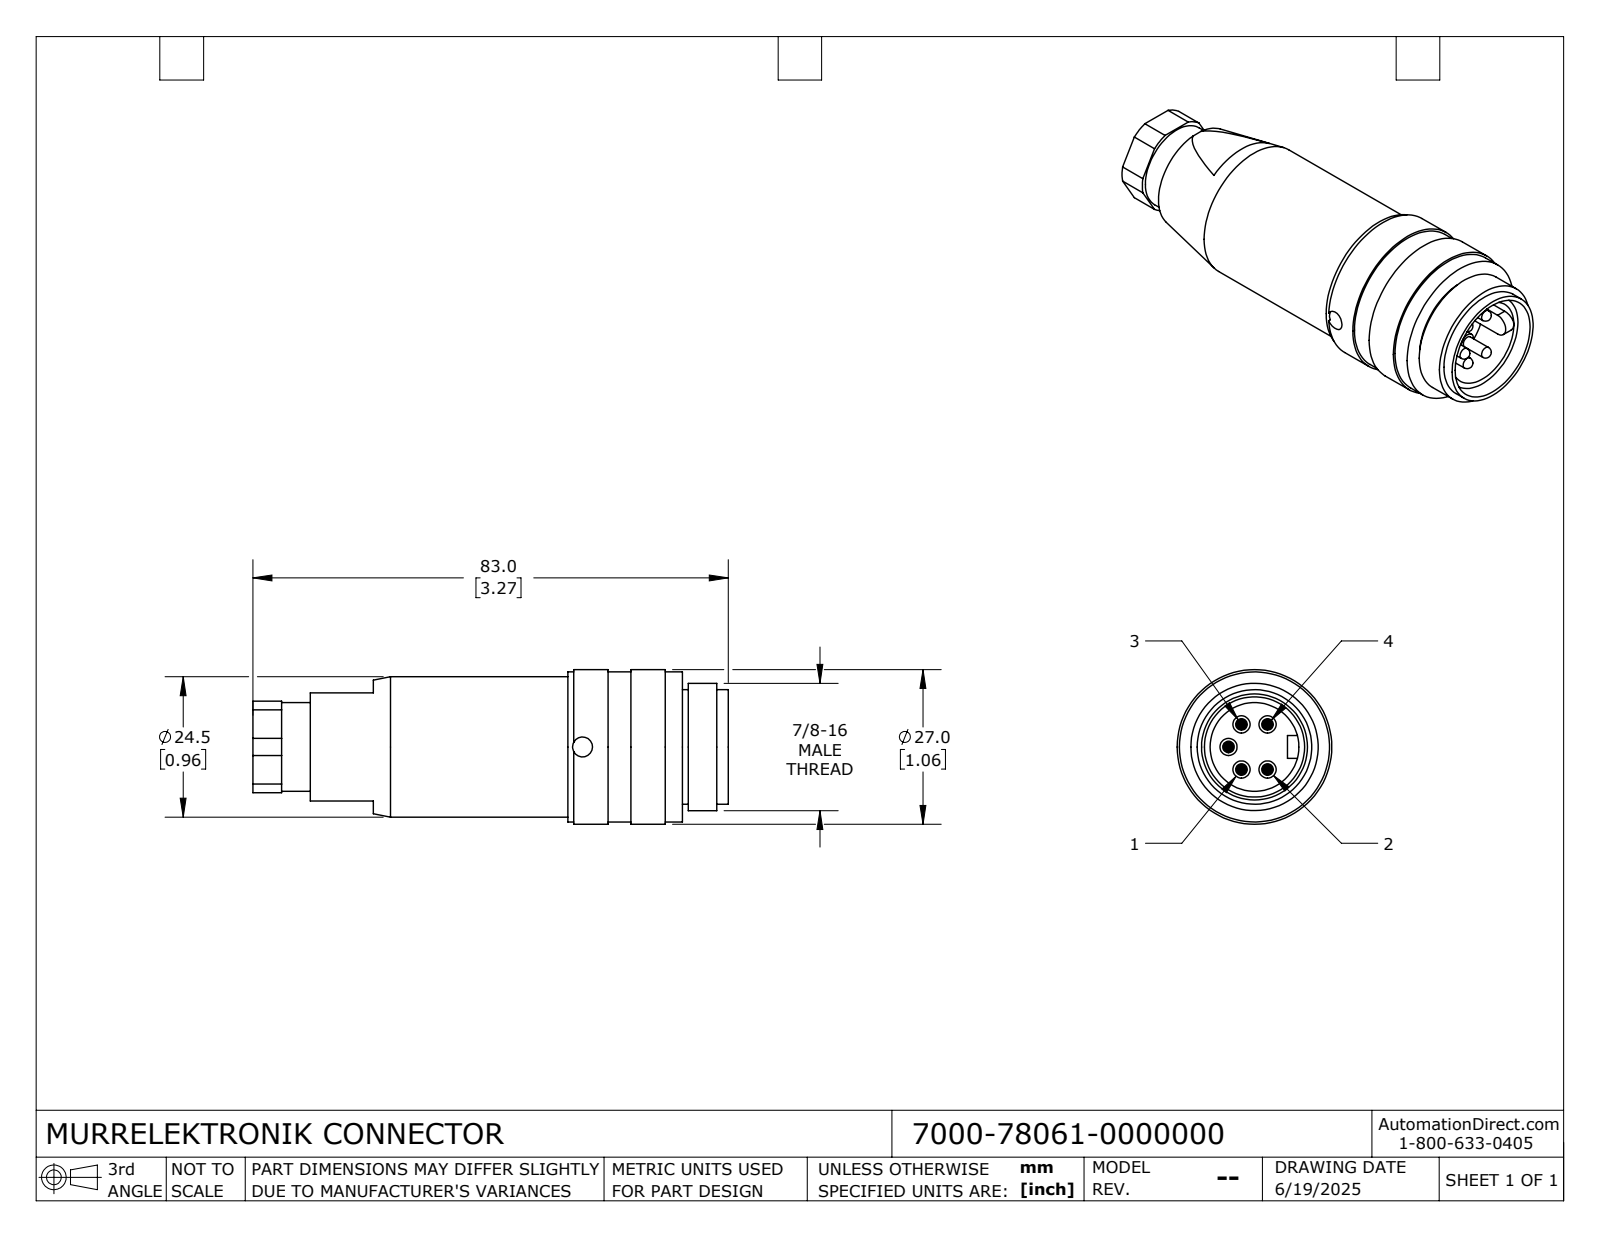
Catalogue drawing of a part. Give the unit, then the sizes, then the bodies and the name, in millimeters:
Units: millimetres
Overall size (bounding box): 83 × 27 × 27
Round holes (diameter × count): ⌀3.5 ×1, ⌀8 ×1, ⌀15.5 ×1, ⌀18.5 ×1
Round bosses / shafts (diameter × count): ⌀3 ×5, ⌀2 ×5, ⌀27 ×1, ⌀26.2 ×1, ⌀24.5 ×1, ⌀22.23 ×1, ⌀20 ×1, ⌀17.5 ×1
Partial cylindrical surfaces — rounded edges, fillets, slot ends (radius × count): R2 ×1, R8.5 ×1
Main face-to-face distances: 10, 2, 73, 6, 75, 16, 21, 11, 1, 5
Volume: 32 256 mm³ · Surface area: 9 725 mm²
Bodies: 1 solid, 103 faces (35 planar, 59 cylindrical, 9 other)
Part name (STEP PRODUCT): 7000-78061-0000000
STEP written by: SolidWorks 2024 (CONFIG_CONTROL_DESIGN)
